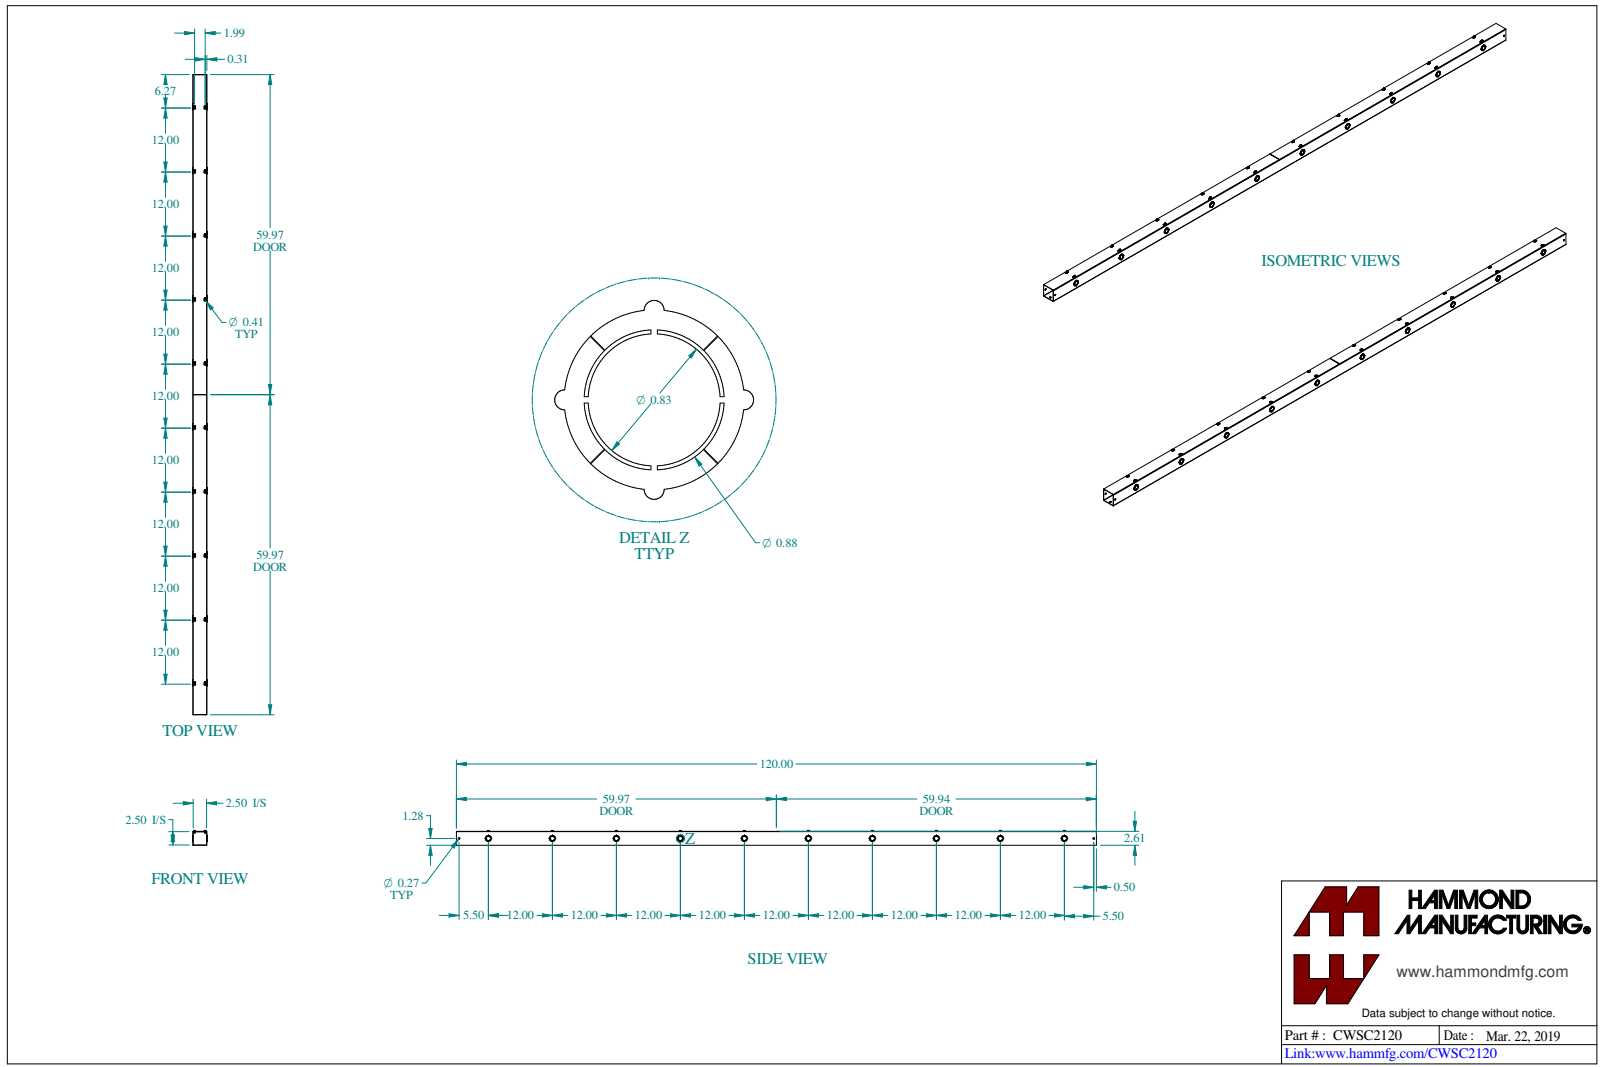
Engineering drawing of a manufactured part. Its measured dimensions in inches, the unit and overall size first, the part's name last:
Units: inches
Overall size (bounding box): 120 × 2.789 × 2.758
Round holes (diameter × count): ⌀0.177 ×20, ⌀0.875 ×10, ⌀0.266 ×2, ⌀0.313 ×2
Round bosses / shafts (diameter × count): ⌀0.375 ×20, ⌀0.19 ×20, ⌀1.125 ×10, ⌀0.825 ×10
Partial cylindrical surfaces — rounded edges, fillets, slot ends (radius × count): R0.062 ×40, R0.125 ×20, R0.203 ×20, R0.029 ×4, R0.086 ×4
Main face-to-face distances: 0.057, 2.557, 2.5, 2.614, 2.443, 0.114, 0.072, 0.129, 2.629, 2.686
Hole centre spacings: 12, 24, 36, 12.164, 48, 24.082, 60, 36.055
Volume: 76.45 in³ · Surface area: 2 675 in²
Bodies: 23 solids, 1514 faces (674 planar, 720 cylindrical, 120 other)
Part name (STEP PRODUCT): CWSC2120
STEP written by: SolidWorks 2023 (CONFIG_CONTROL_DESIGN)
